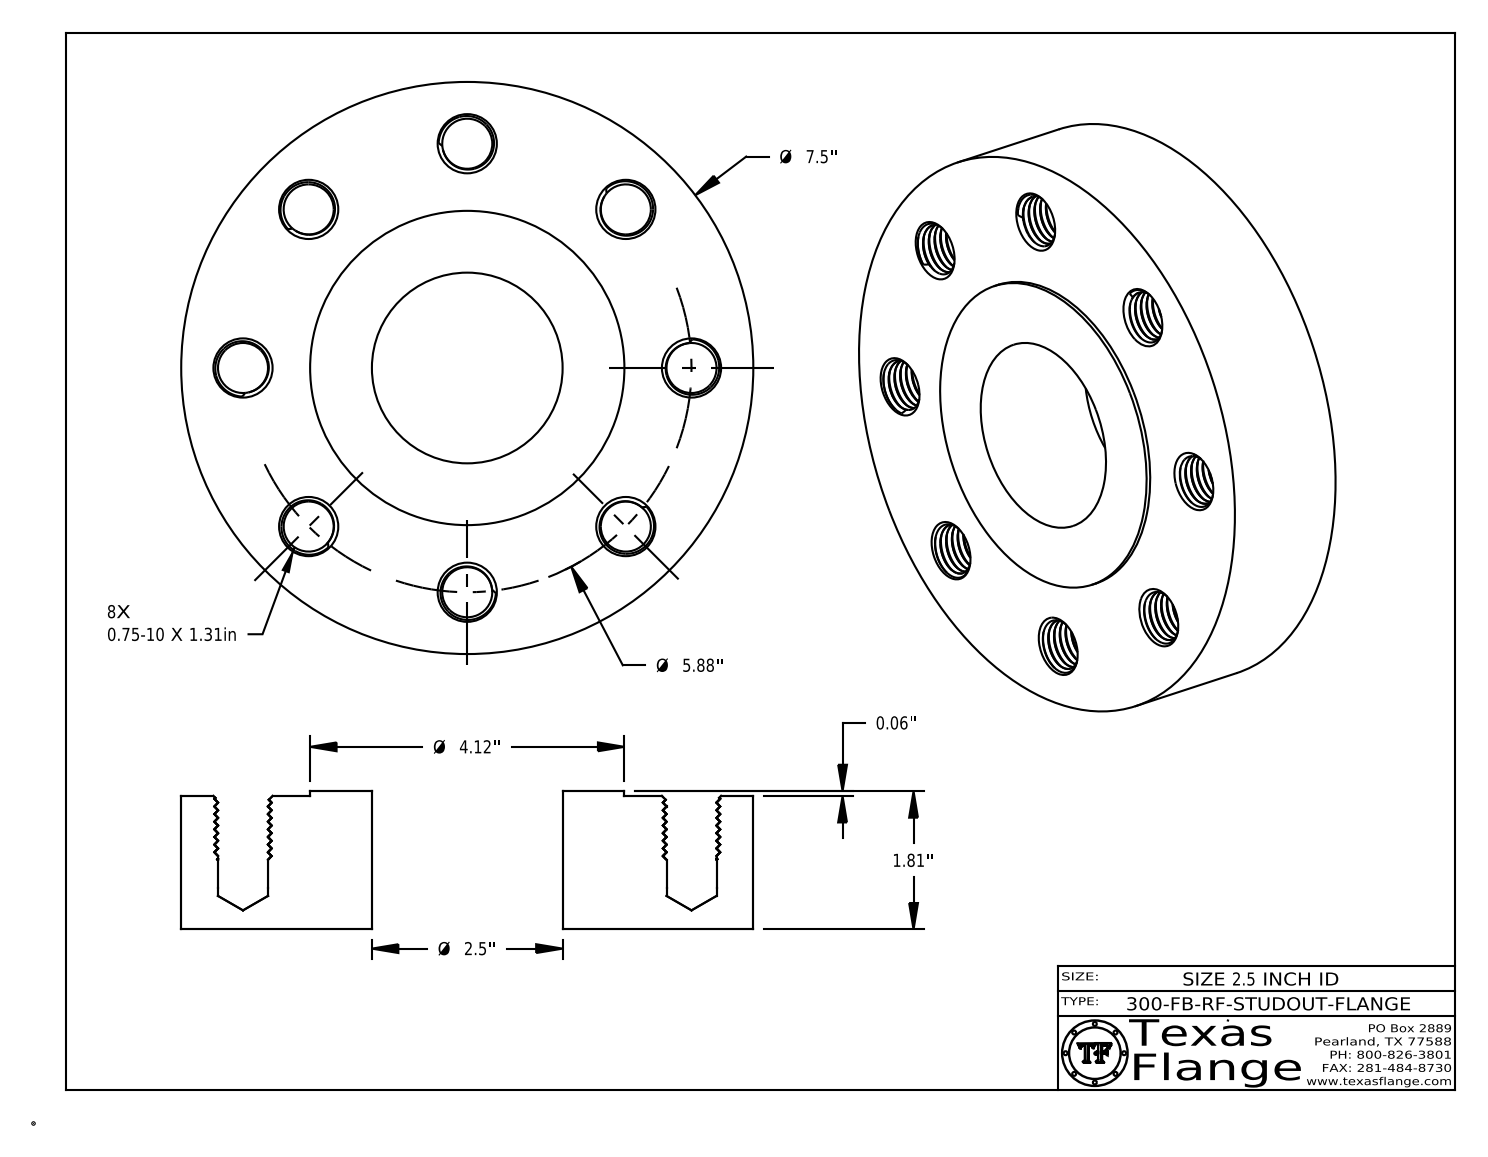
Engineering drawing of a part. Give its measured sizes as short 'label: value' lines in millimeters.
name: 2.5-300-FB-RF-STUDOUT-FLANGE
written by: CATIA V5 STEP AP214 (AUTOMOTIVE_DESIGN)
unit: mm
bodies: 1 solid, 874 faces (368 planar, 186 cylindrical, 320 other)
size: 190.5 × 190.5 × 46.1
volume: 1 068 000 mm³; area: 104 900 mm²
holes: 8× ⌀16.7, 1× ⌀25.4, 1× ⌀63.5
bosses: 8× ⌀1.5, 1× ⌀190.5, 1× ⌀104.6, 1× ⌀20
face distances: 44.5, 1.6, 46.1, 0.4, 45.7, 44.1, 7.6, 7.4, 1.4, 6.3
hole spacings: 57.2, 138, 74.7, 74.7, 105.6, 105.6, 149.4, 149.4
